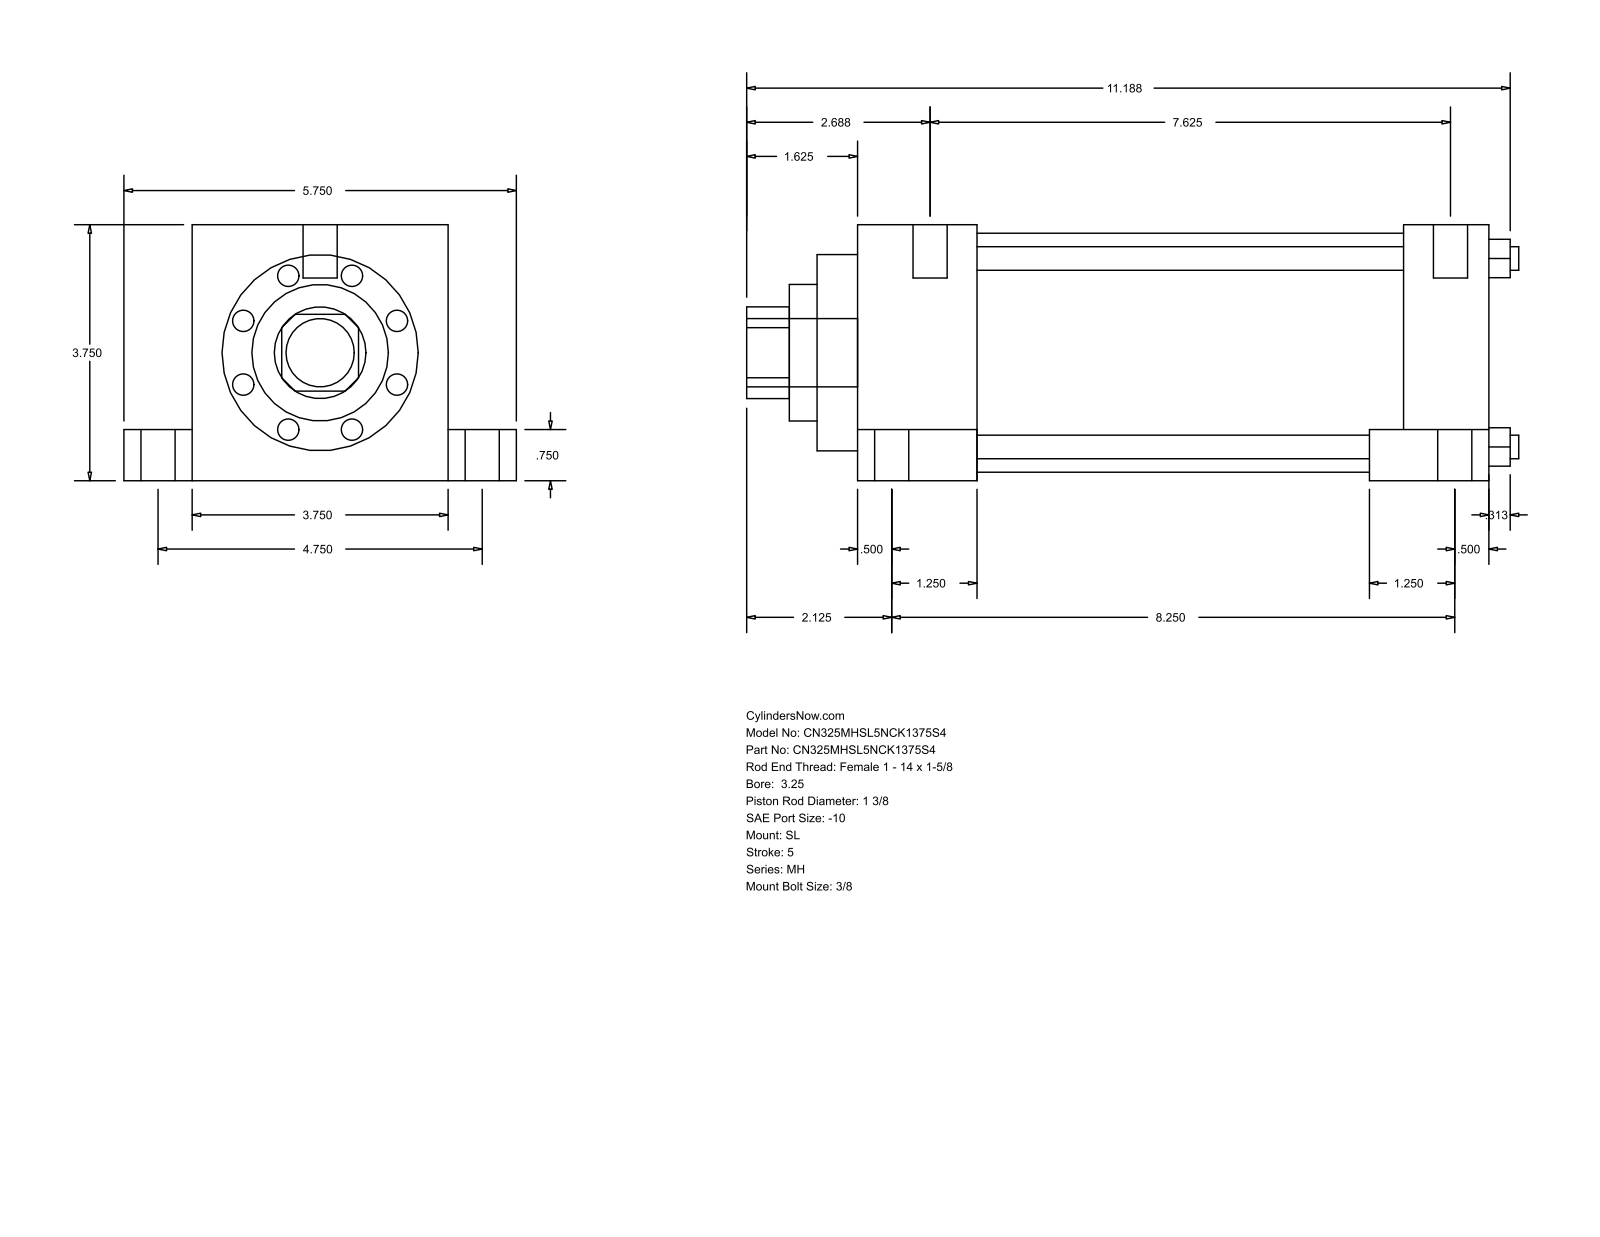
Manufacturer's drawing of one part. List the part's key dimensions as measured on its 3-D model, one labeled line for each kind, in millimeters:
Part name (STEP PRODUCT): MH_SL__0325_1.375
STEP written by: GSSL Pune (CONFIG_CONTROL_DESIGN)
Units: millimetres
Bodies: 0 solids, 110 faces (77 planar, 33 cylindrical, 0 other)
Overall size (bounding box): 287.34 × 146.05 × 95.25
Round holes (diameter × count): ⌀8.76 ×4, ⌀34.92 ×1, ⌀50.8 ×1, ⌀73.03 ×1, ⌀88.9 ×1
Round bosses / shafts (diameter × count): ⌀12.7 ×6, ⌀19.05 ×4, ⌀5.56 ×4, ⌀25.4 ×1
Partial cylindrical surfaces — rounded edges, fillets, slot ends (radius × count): R17.06 ×1
Main face-to-face distances: 95.24, 234.96, 44.45, 190.51, 25.41, 120.65, 19.05, 76.19, 146.06, 203.2
Hole centre spacings: 49.57, 70.1, 99.14
